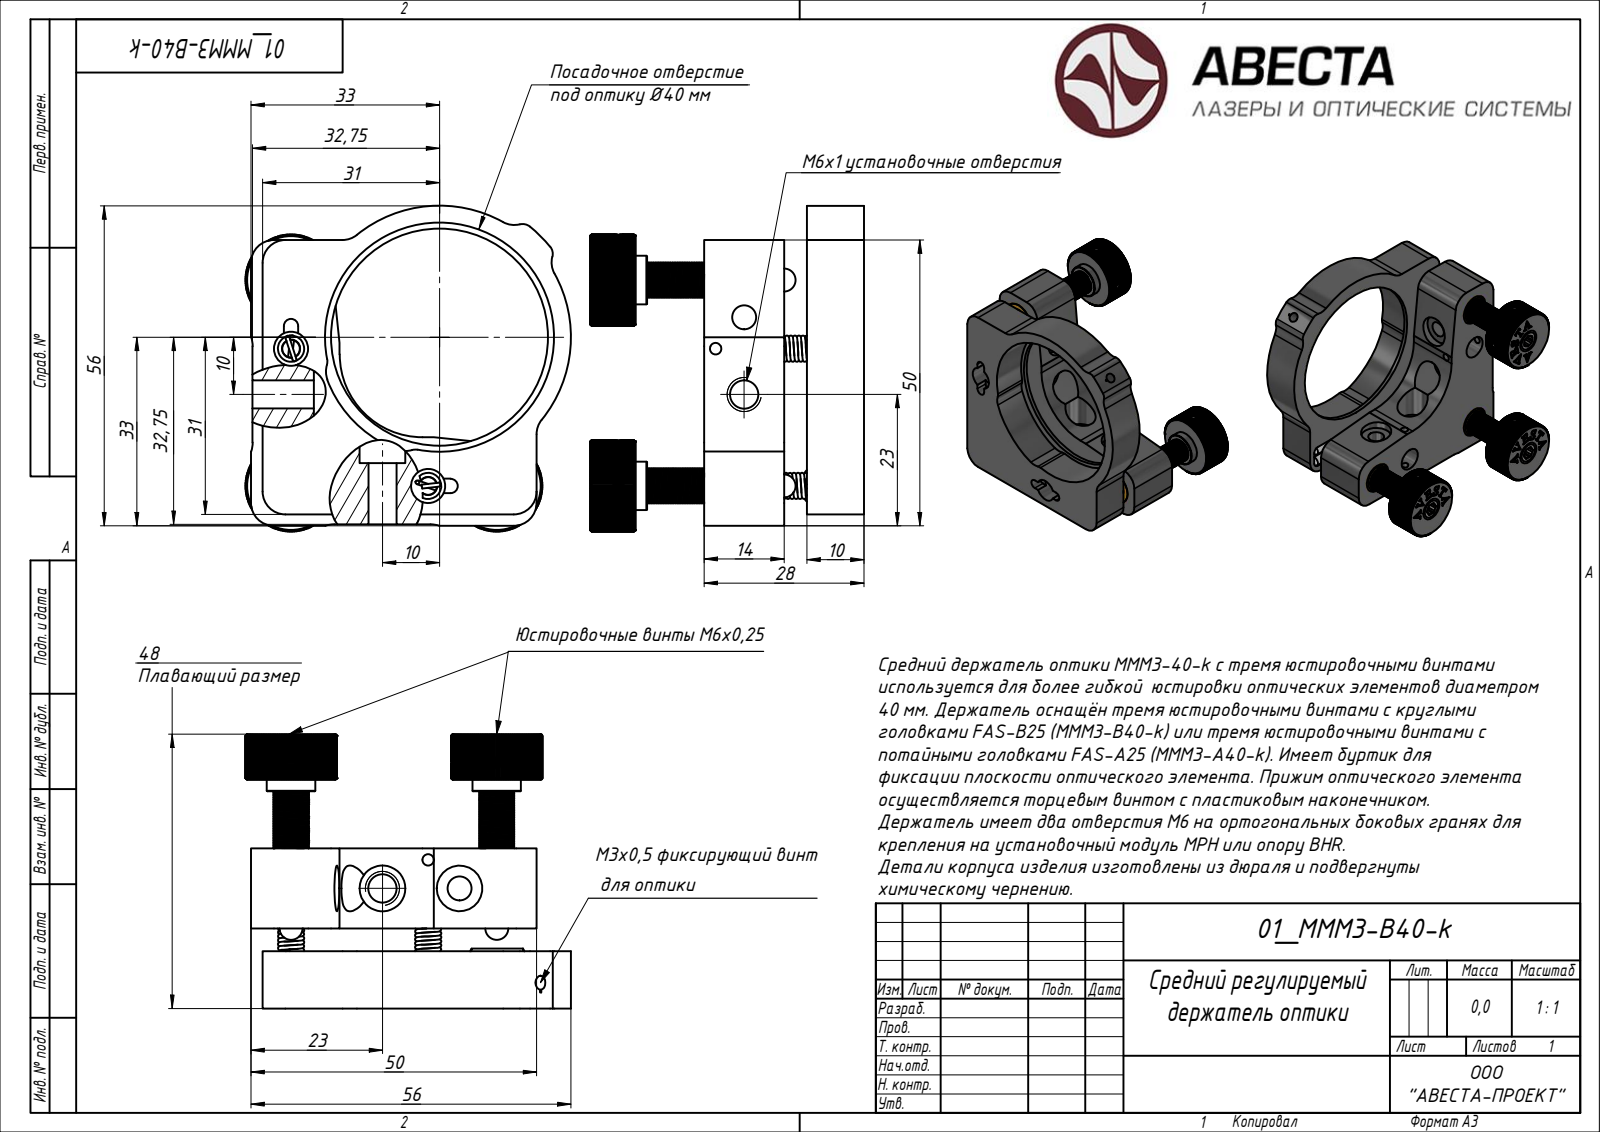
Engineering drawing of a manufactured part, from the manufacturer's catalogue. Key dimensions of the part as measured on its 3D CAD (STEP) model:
STEP written by: ST-DEVELOPER v15 (AUTOMOTIVE_DESIGN)
Units: millimetres
Bodies: 14 solids, 842 faces (409 planar, 0 cylindrical, 433 other)
Overall size (bounding box): 57 × 57 × 44.2
Volume: 33 798 mm³ · Surface area: 21 453 mm²
Main face-to-face distances: 14, 10, 28, 4, 18, 2, 8, 1.75, 48, 49.75
